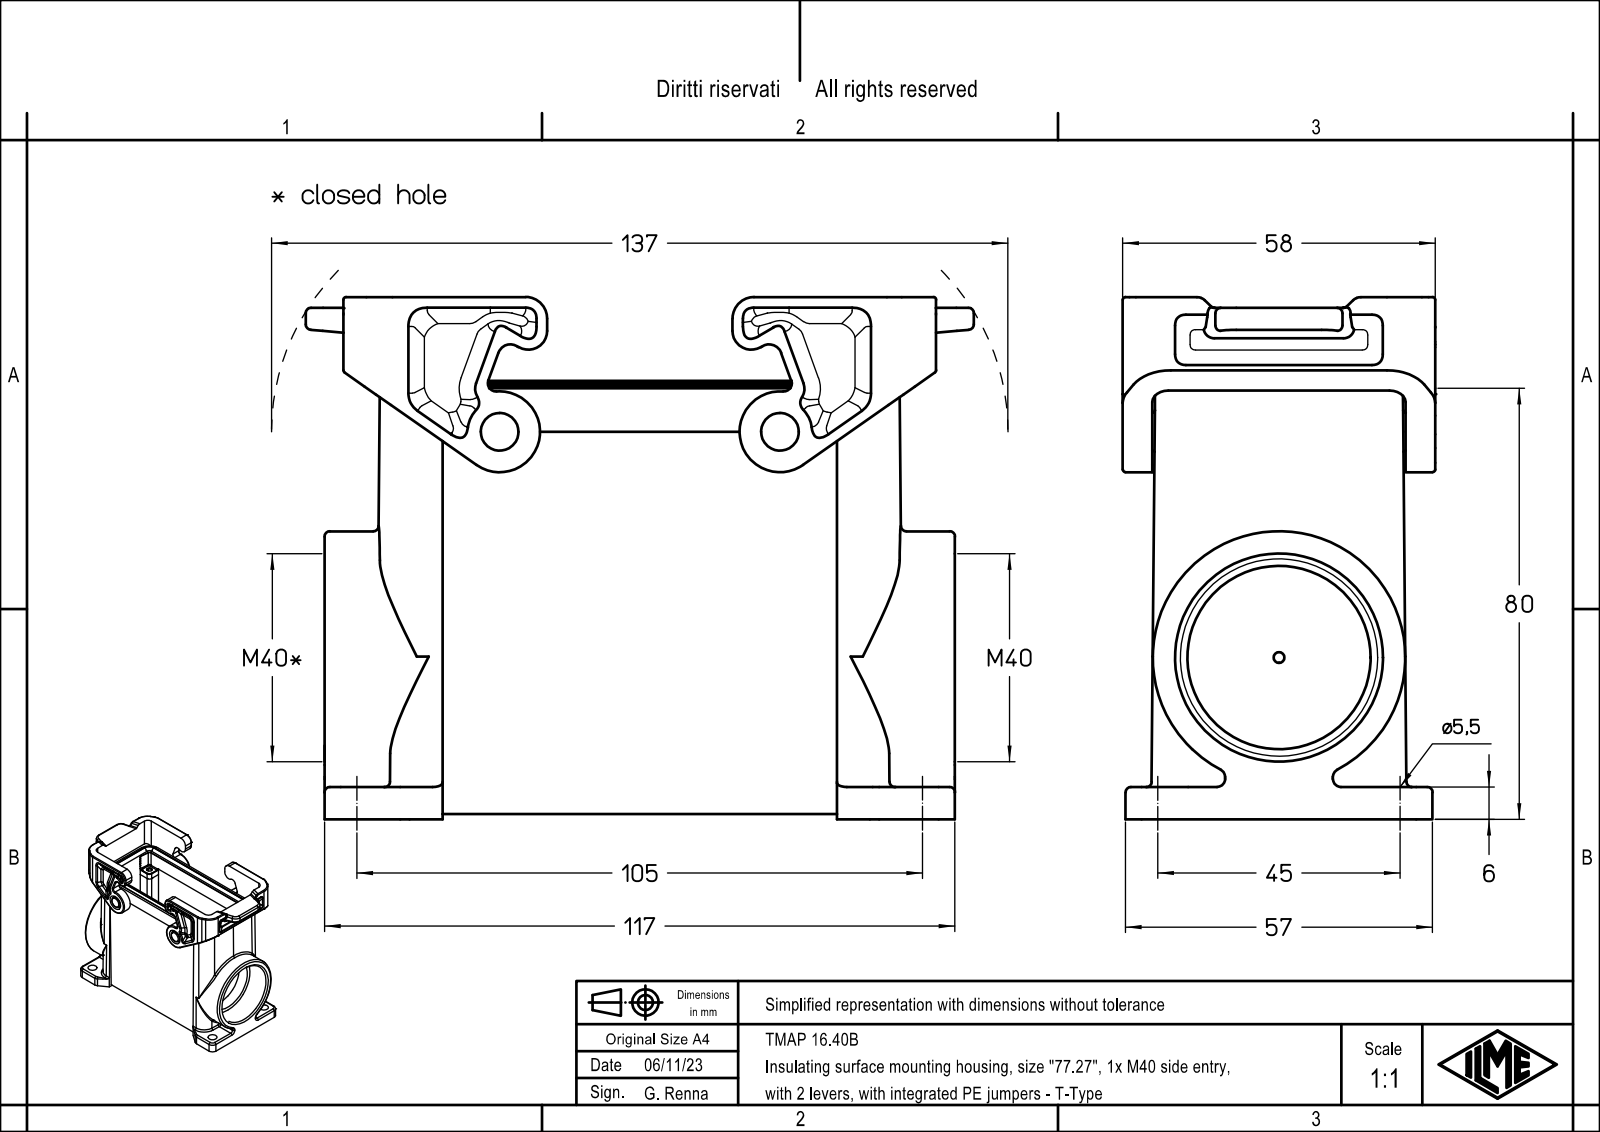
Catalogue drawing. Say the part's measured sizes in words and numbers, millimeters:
The part is named "TMAP 16.40B". Its 3-D file was written by "Creo Elements/Direct Modeling 20.1B 02-Apr-2019 (C) Parametric Technology GmbH (AUTOMOTIVE_DESIGN)". It is 1 solid with 610 faces: 364 planar, 194 cylindrical and 52 other. Overall it measures 124 by 96.9 by 58 millimeters. Its volume is 180 659 cubic millimeters and its surface area 74 064 square millimeters. Round holes: 4 of diameter 3.5, 4 of diameter 5.5, 1 of diameter 34, 1 of diameter 38.6. Round bosses or shafts: 2 of diameter 7, 1 of diameter 46.87. Partial cylindrical surfaces (rounded edges, fillets, slot ends): 20 of radius 2, 20 of radius 3, 18 of radius 1.5, 16 of radius 1, 12 of radius 1.3, 8 of radius 6, 8 of radius 7, 6 of radius 4. The main face-to-face distances are 35.2, 5.5, 5.9, 41.1, 1, 6.5, 11.4, 46.6, 52.5, 11.8. The hole center spacings are 16.43, 38.54, 91.69, 98.09, 27, 45, 77.5, 82.07.
